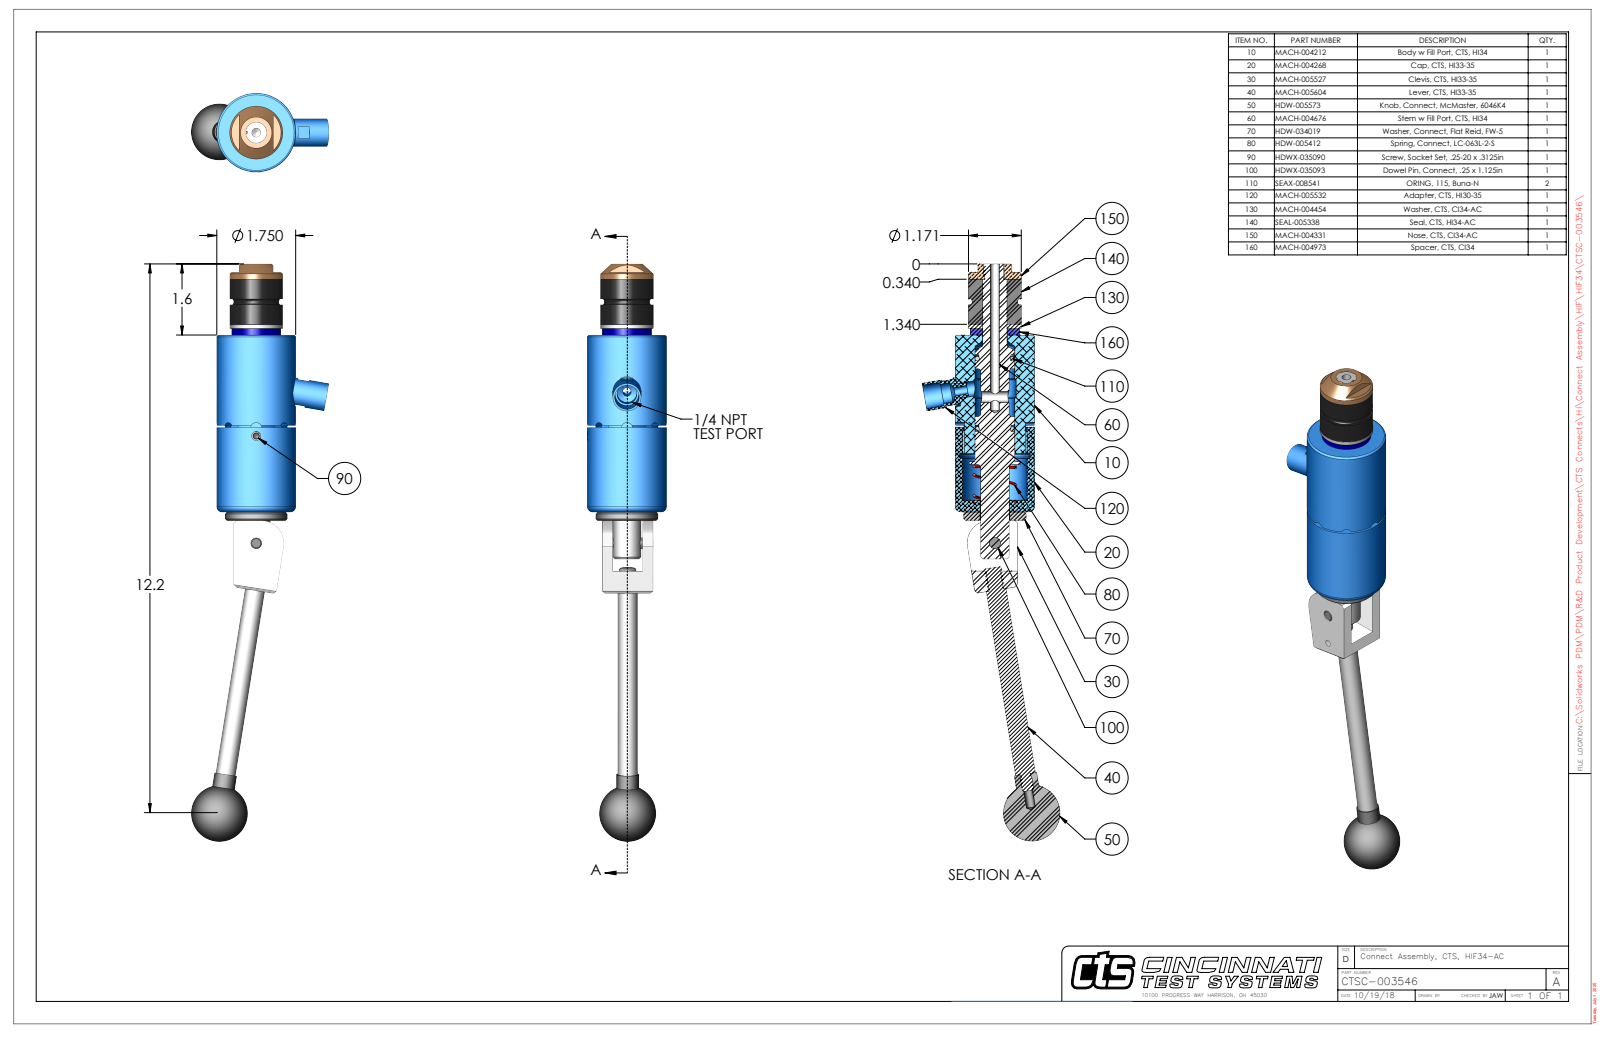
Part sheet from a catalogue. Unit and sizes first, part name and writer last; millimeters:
Units: millimetres
Overall size (bounding box): 325 × 77.3 × 44.5
Round holes (diameter × count): ⌀5.1 ×2, ⌀3.8 ×1, ⌀4.7 ×1, ⌀5.2 ×1, ⌀6.3 ×1, ⌀6.4 ×1, ⌀6.4 ×1, ⌀8 ×1, ⌀10.7 ×1, ⌀11.1 ×1, ⌀13.5 ×1, ⌀13.7 ×1
Round bosses / shafts (diameter × count): ⌀12.7 ×2, ⌀11.2 ×2, ⌀6.4 ×2, ⌀44.5 ×1, ⌀35.1 ×1, ⌀29.7 ×1, ⌀27.7 ×1, ⌀15.9 ×1
Partial cylindrical surfaces — rounded edges, fillets, slot ends (radius × count): R3.2 ×4, R0.7 ×2, R4.2 ×1, R4.6 ×1, R8.4 ×1, R12.7 ×1, R17.7 ×1, R20.8 ×1
Main face-to-face distances: 99.6, 31.4, 131, 25.4, 6, 105.6, 27.8, 2.4, 3.6, 103.2
Hole centre spacings: 18.8, 60.4, 79.1
Volume: 231 400 mm³ · Surface area: 51 840 mm²
Bodies: 10 solids, 298 faces (106 planar, 125 cylindrical, 67 other)
Part name (STEP PRODUCT): CTSC-003546
STEP written by: SolidWorks 2023 (AUTOMOTIVE_DESIGN)
